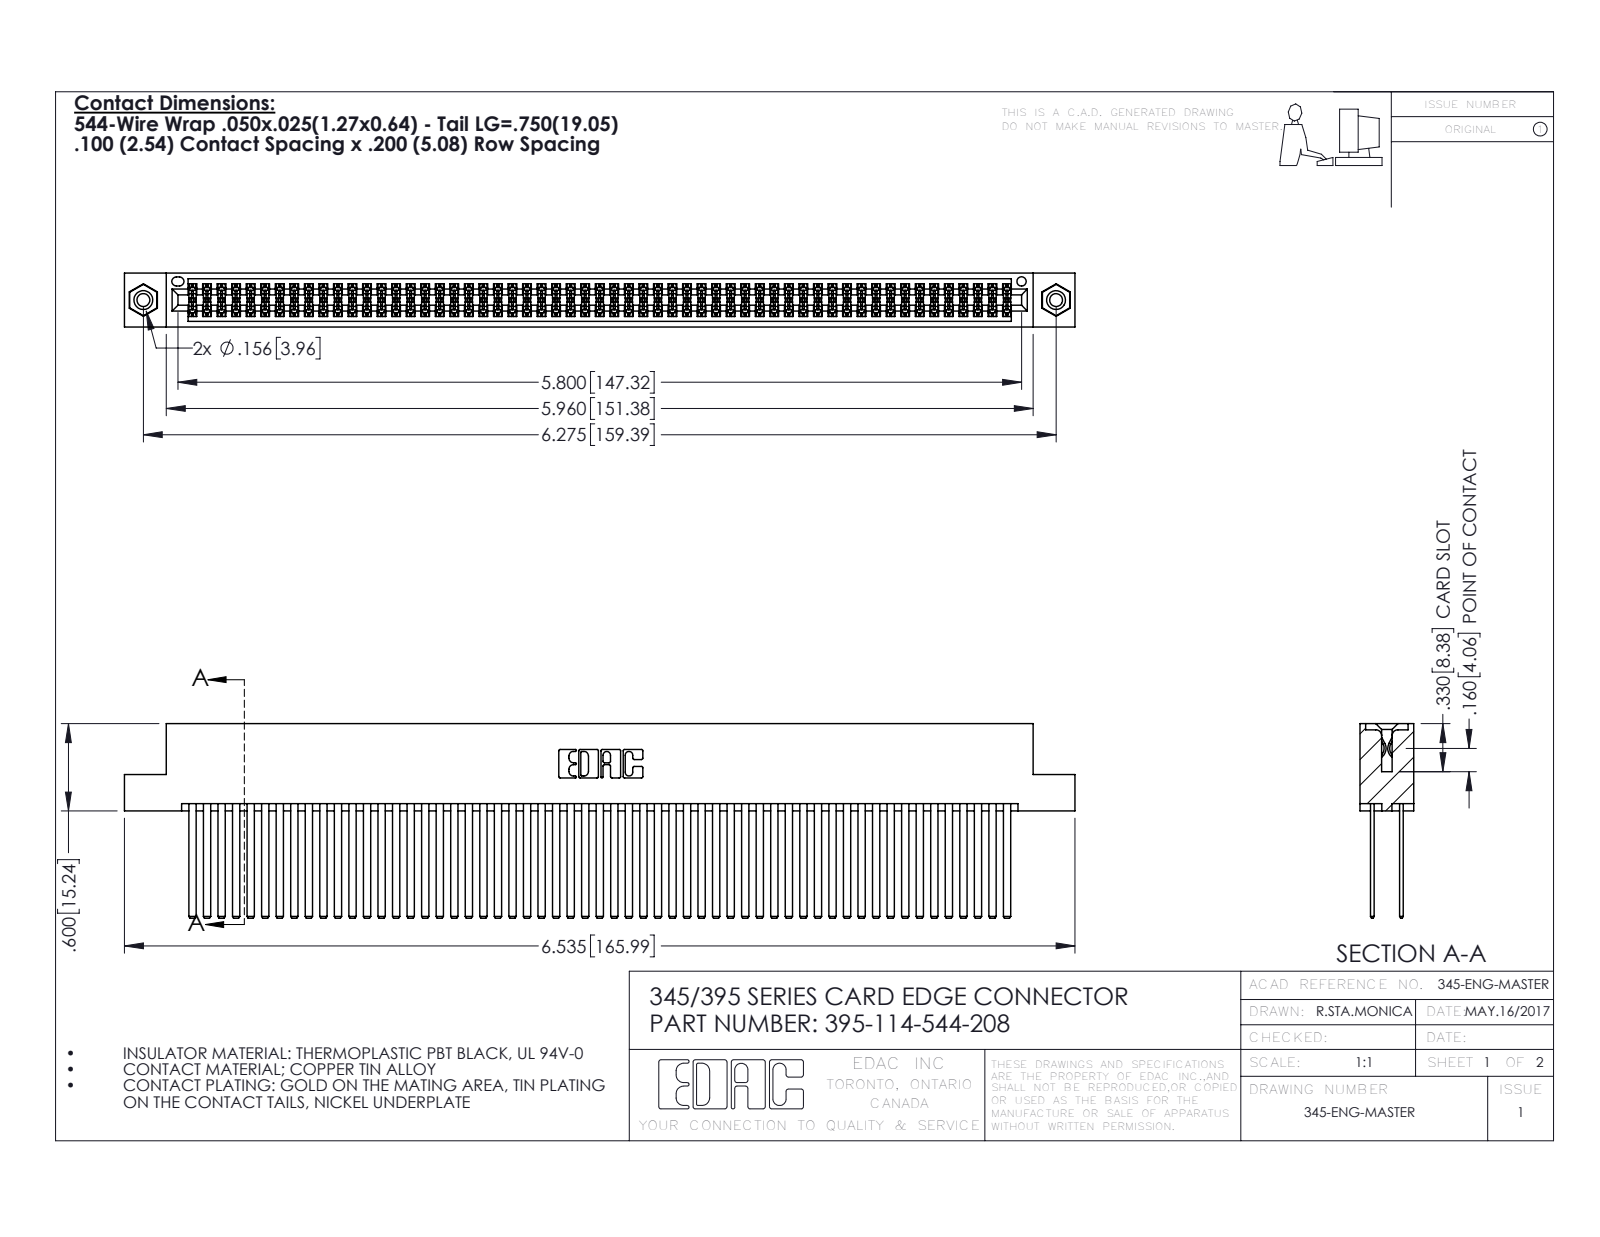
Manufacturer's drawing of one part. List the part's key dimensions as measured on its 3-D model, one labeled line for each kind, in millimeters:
Part name (STEP PRODUCT): 395-114-544-208; 345-250-001_345-250-003-102; 345 Part_Flush Mounting Lugs - 0.156 Dia-TI; 345-292-001_345-293-144
STEP written by: SolidWorks 2016 (CONFIG_CONTROL_DESIGN)
Units: millimetres
Bodies: 117 solids, 5202 faces (3418 planar, 1768 cylindrical, 16 other)
Overall size (bounding box): 166 × 34 × 9.4
Volume: 17 860 mm³ · Surface area: 31 380 mm²
Round holes (diameter × count): ⌀2.3 ×2, ⌀3.2 ×2, ⌀4 ×2, ⌀1.6 ×1
Round bosses / shafts (diameter × count): ⌀3.9 ×2
Partial cylindrical surfaces — rounded edges, fillets, slot ends (radius × count): R0.2 ×171, R0.3 ×22, R0.2 ×6, R0.8 ×6, R0.7 ×3, R0.4 ×2, R0.5 ×2, R0.6 ×2
Main face-to-face distances: 5.1, 0.6, 1.8, 2.5, 6.9, 7.6, 5.7, 4.4, 9.4, 1.3
Hole centre spacings: 6.9, 153.4, 159.4
